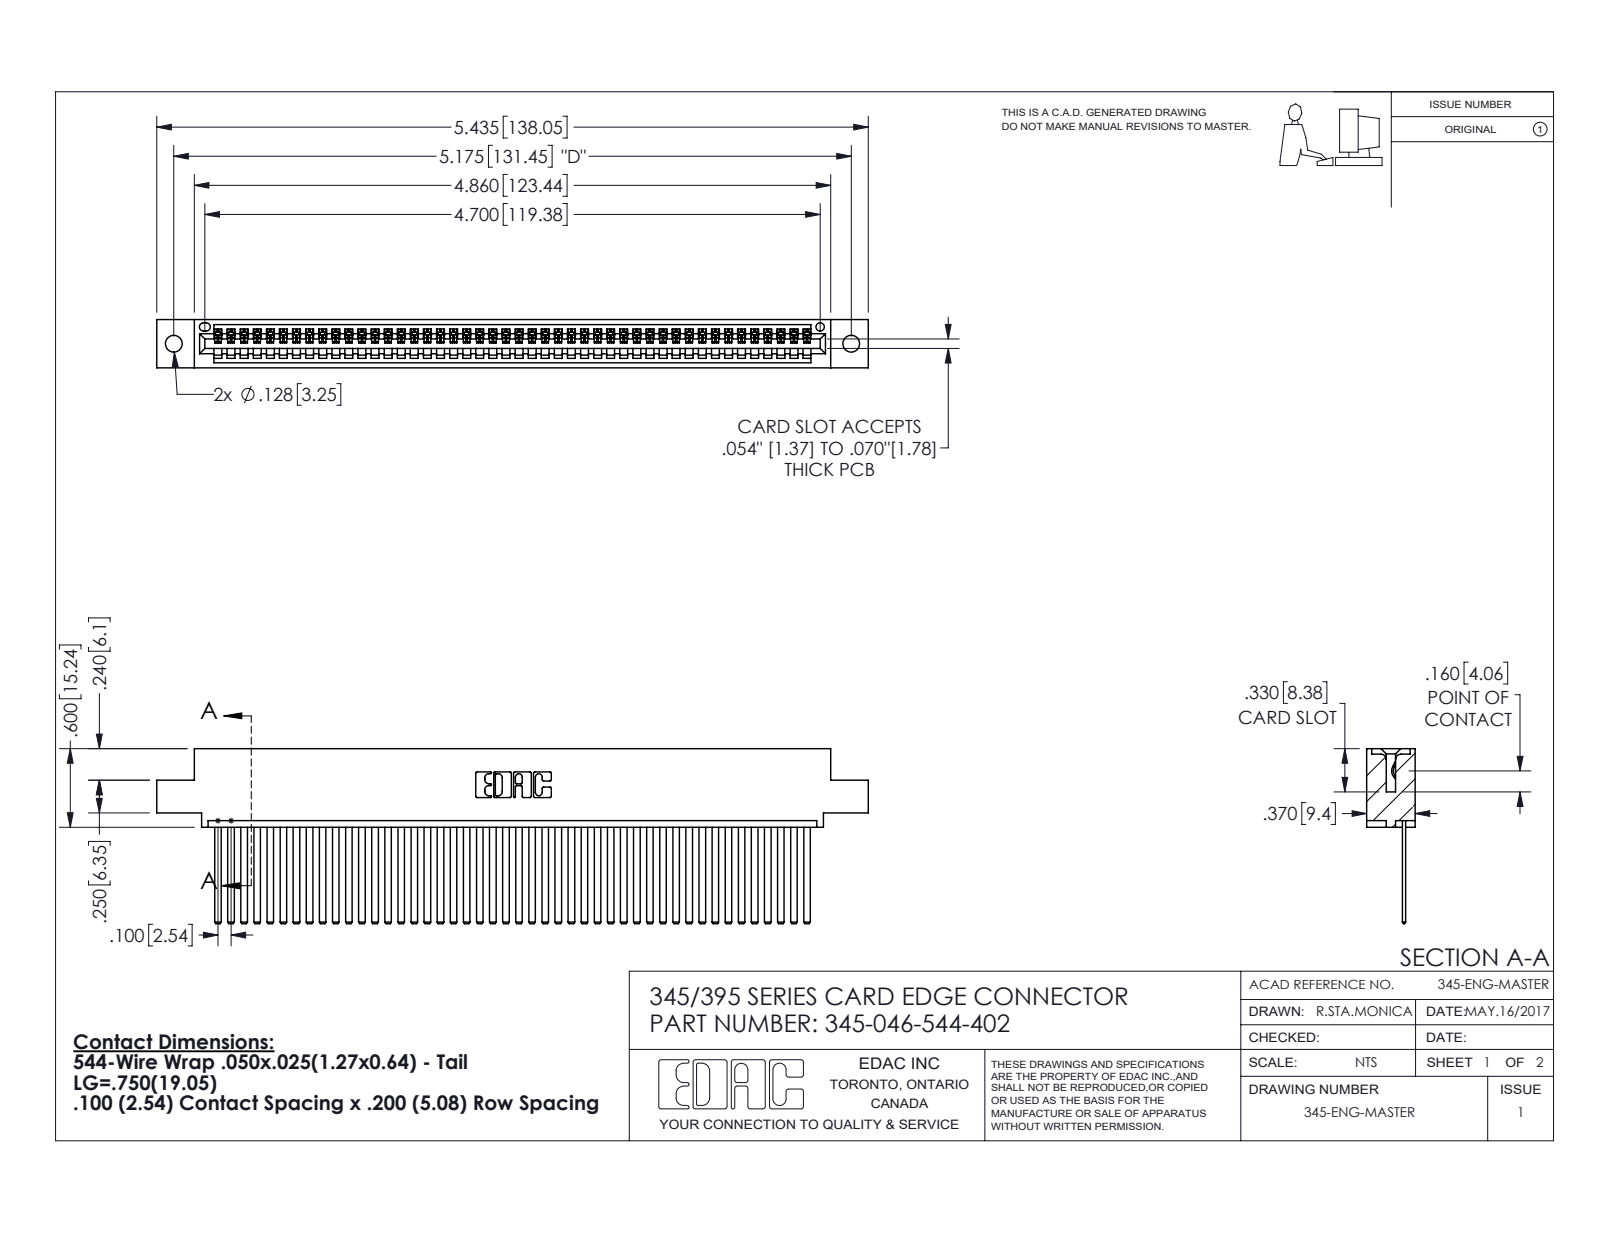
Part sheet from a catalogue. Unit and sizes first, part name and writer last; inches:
Units: inches
Overall size (bounding box): 5.435 × 1.337 × 0.37
Round holes (diameter × count): ⌀0.128 ×2, ⌀0.064 ×1
Partial cylindrical surfaces — rounded edges, fillets, slot ends (radius × count): R0.006 ×92, R0.01 ×22, R0.007 ×6, R0.031 ×6, R0.026 ×3, R0.031 ×2, R0.04 ×2, R0.014 ×1
Main face-to-face distances: 0.072, 0.298, 0.025, 0.098, 0.272, 0.37, 0.2, 0.225, 0.149, 0.072
Hole centre spacings: 0.27, 4.939, 5.175
Volume: 0.828 in³ · Surface area: 30.22 in²
Bodies: 47 solids, 2522 faces (1740 planar, 782 cylindrical, 0 other)
Part name (STEP PRODUCT): 345-046-544-402; 345 Part_0.110 Offset - 0.128 Dia; 345-292-001_345-293-144
STEP written by: SolidWorks 2016 (CONFIG_CONTROL_DESIGN)
